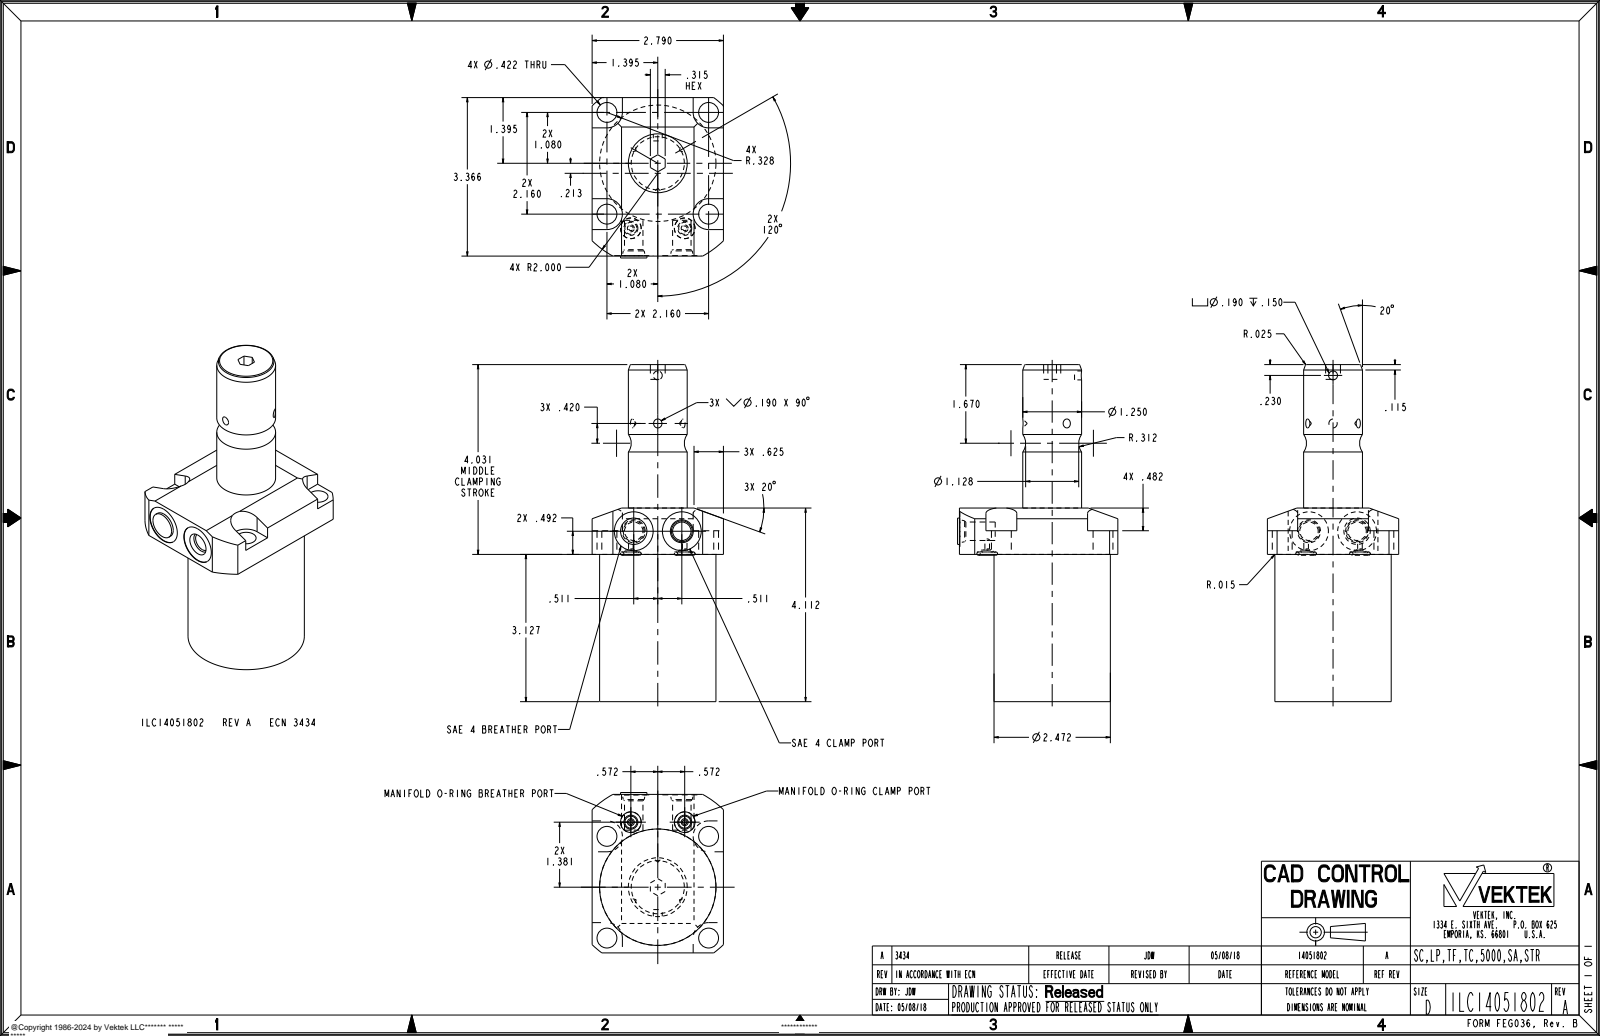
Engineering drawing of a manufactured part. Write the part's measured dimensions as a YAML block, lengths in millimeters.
part_name: "ILC14051802"
step_written_by: "PRO/ENGINEER BY PARAMETRIC TECHNOLOGY CORPORATION, 2013320 (AUTOMOTIVE_DESIGN)"
units: millimeters
bodies: {solids: 3, faces: 123, planar: 43, cylindrical: 46, other: 34}
overall_size: [181.8, 86.5, 70.9]
volume: 428400
surface_area: 45410
round_holes:
  - {diameter: 10.7, count: 4}
  - {diameter: 2.5, count: 2}
  - {diameter: 6.5, count: 2}
  - {diameter: 10, count: 2}
  - {diameter: 11.1, count: 2}
  - {diameter: 21, count: 2}
  - {diameter: 4.8, count: 1}
round_bosses_or_shafts:
  - {diameter: 62.8, count: 1}
  - {diameter: 31.8, count: 1}
  - {diameter: 14.2, count: 1}
partial_cylinders:
  - {radius: 8.3, count: 4}
  - {radius: 50.8, count: 1}
face_to_face_distances: [79.4, 104.4, 25, 70.9, 92.2, 12.8, 12.2, 181.8, 102.4, 89.6]
hole_center_spacings: [54.9, 15, 42.6, 63.8, 75.3, 77.6, 85, 26]
